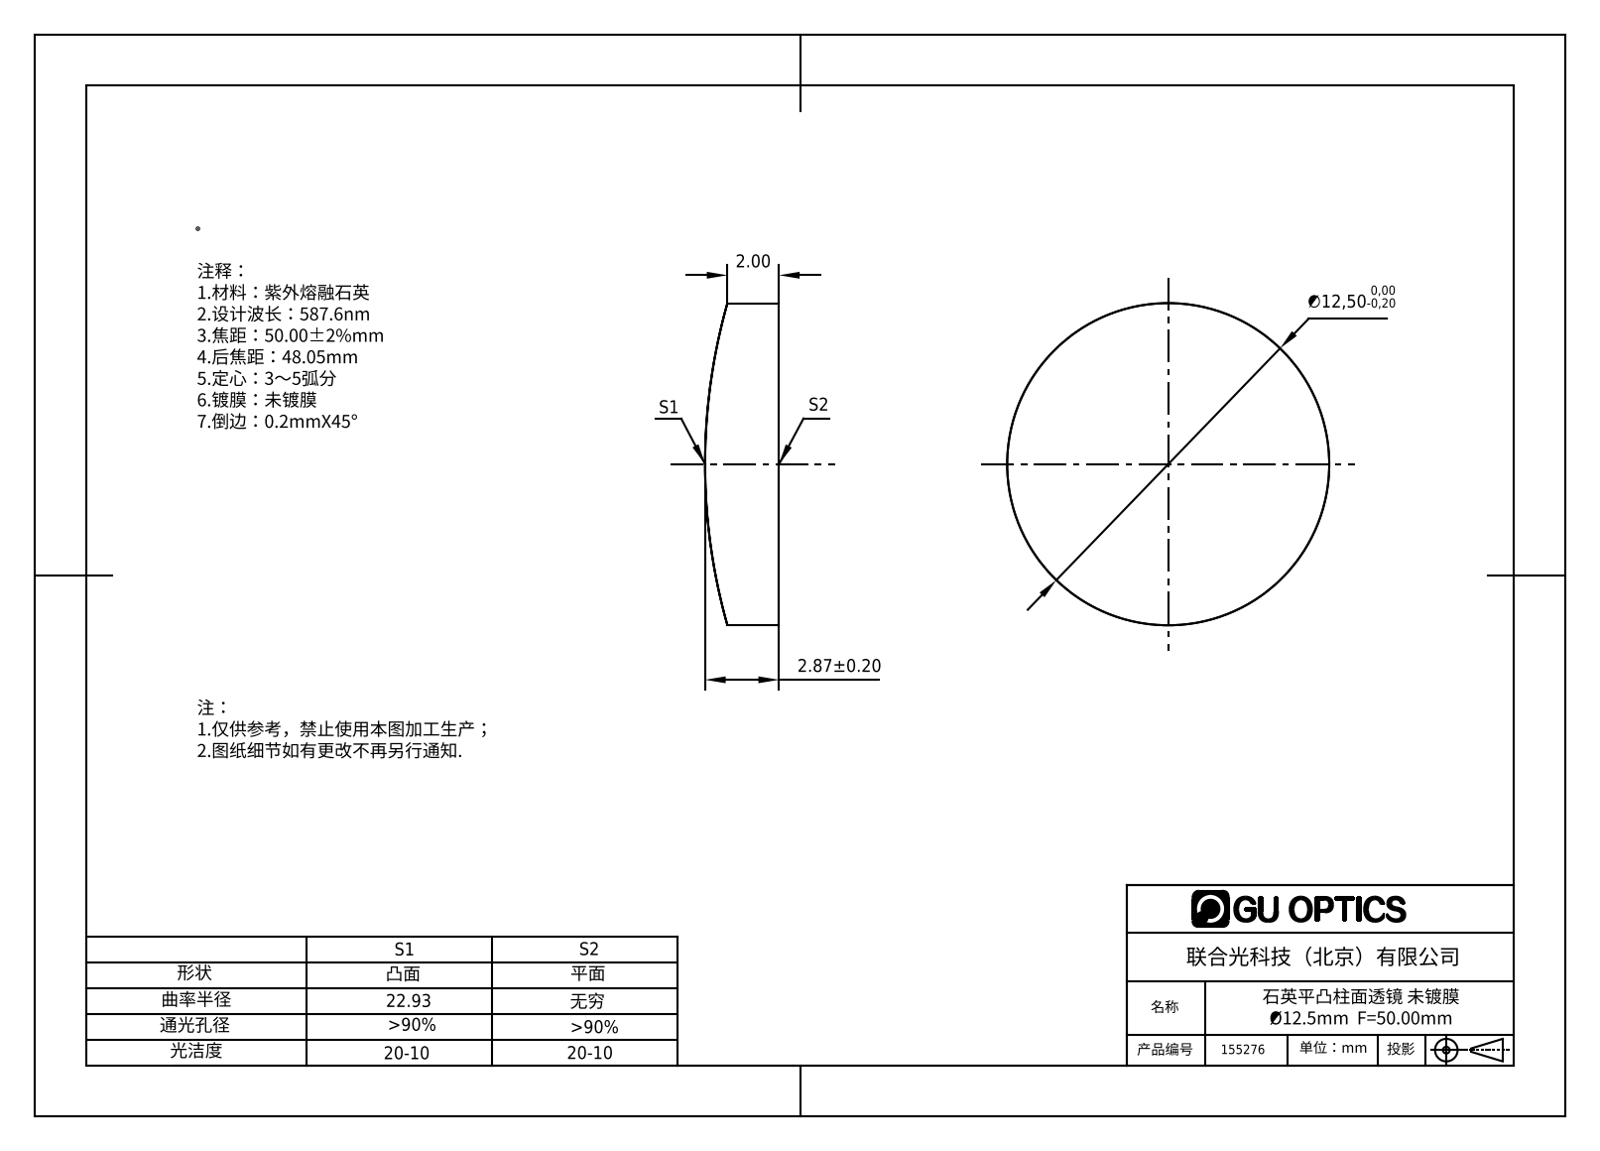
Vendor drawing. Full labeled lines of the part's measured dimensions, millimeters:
Part name (STEP PRODUCT): 155276
STEP written by: SolidWorks 2016 (AUTOMOTIVE_DESIGN)
Units: millimetres
Bodies: 1 solid, 4 faces (1 planar, 3 cylindrical, 0 other)
Overall size (bounding box): 12.5 × 12.5 × 2.87
Volume: 326 mm³ · Surface area: 342 mm²
Round bosses / shafts (diameter × count): ⌀12.5 ×1
Partial cylindrical surfaces — rounded edges, fillets, slot ends (radius × count): R22.93 ×1
